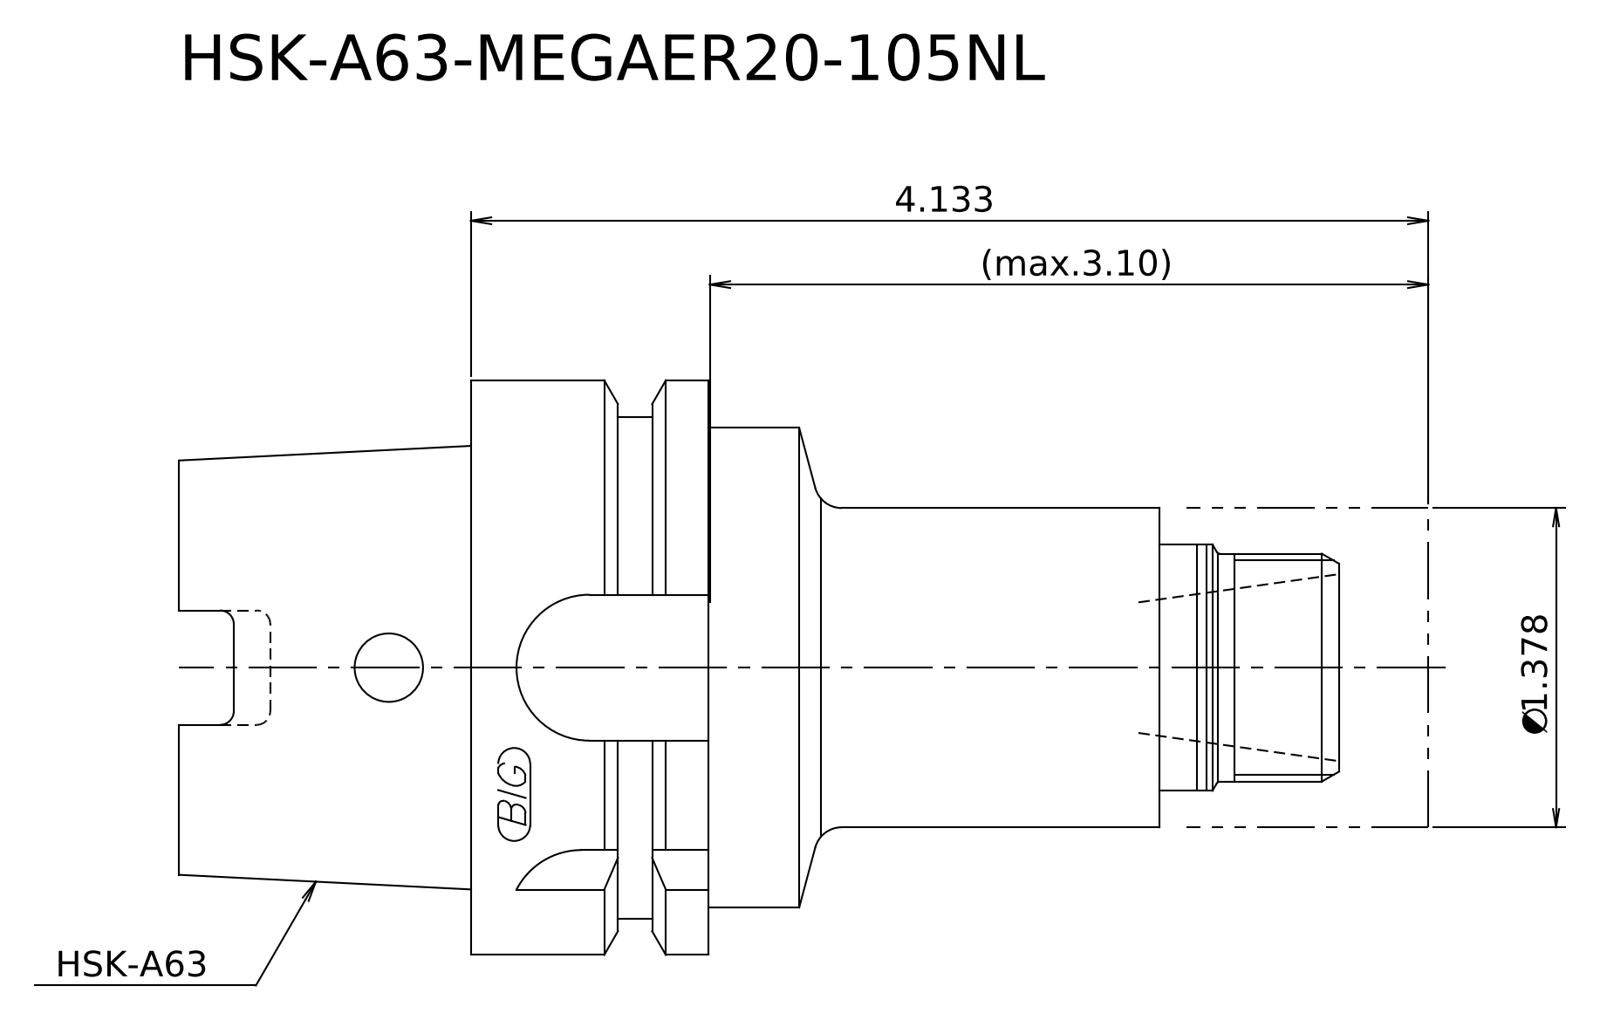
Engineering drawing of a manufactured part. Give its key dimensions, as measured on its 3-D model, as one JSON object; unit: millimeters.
{"step_written_by": "Kubotek KeyCreator 2011 V10.0.2 (22737) (automotive_design)", "units": "millimeters", "bodies": {"solids": 2, "faces": 23, "planar": 9, "cylindrical": 8, "other": 6}, "overall_size": [137, 63, 63], "volume_mm3": 231077, "surface_area_mm2": 28789, "round_bosses_or_shafts": [[63, 1], [55, 1], [52.6, 1], [35, 1], [27, 1], [25, 1]], "face_to_face_distances": [32, 78.5, 110.5, 26.5, 105, 137, 79, 52.5, 26, 58]}
